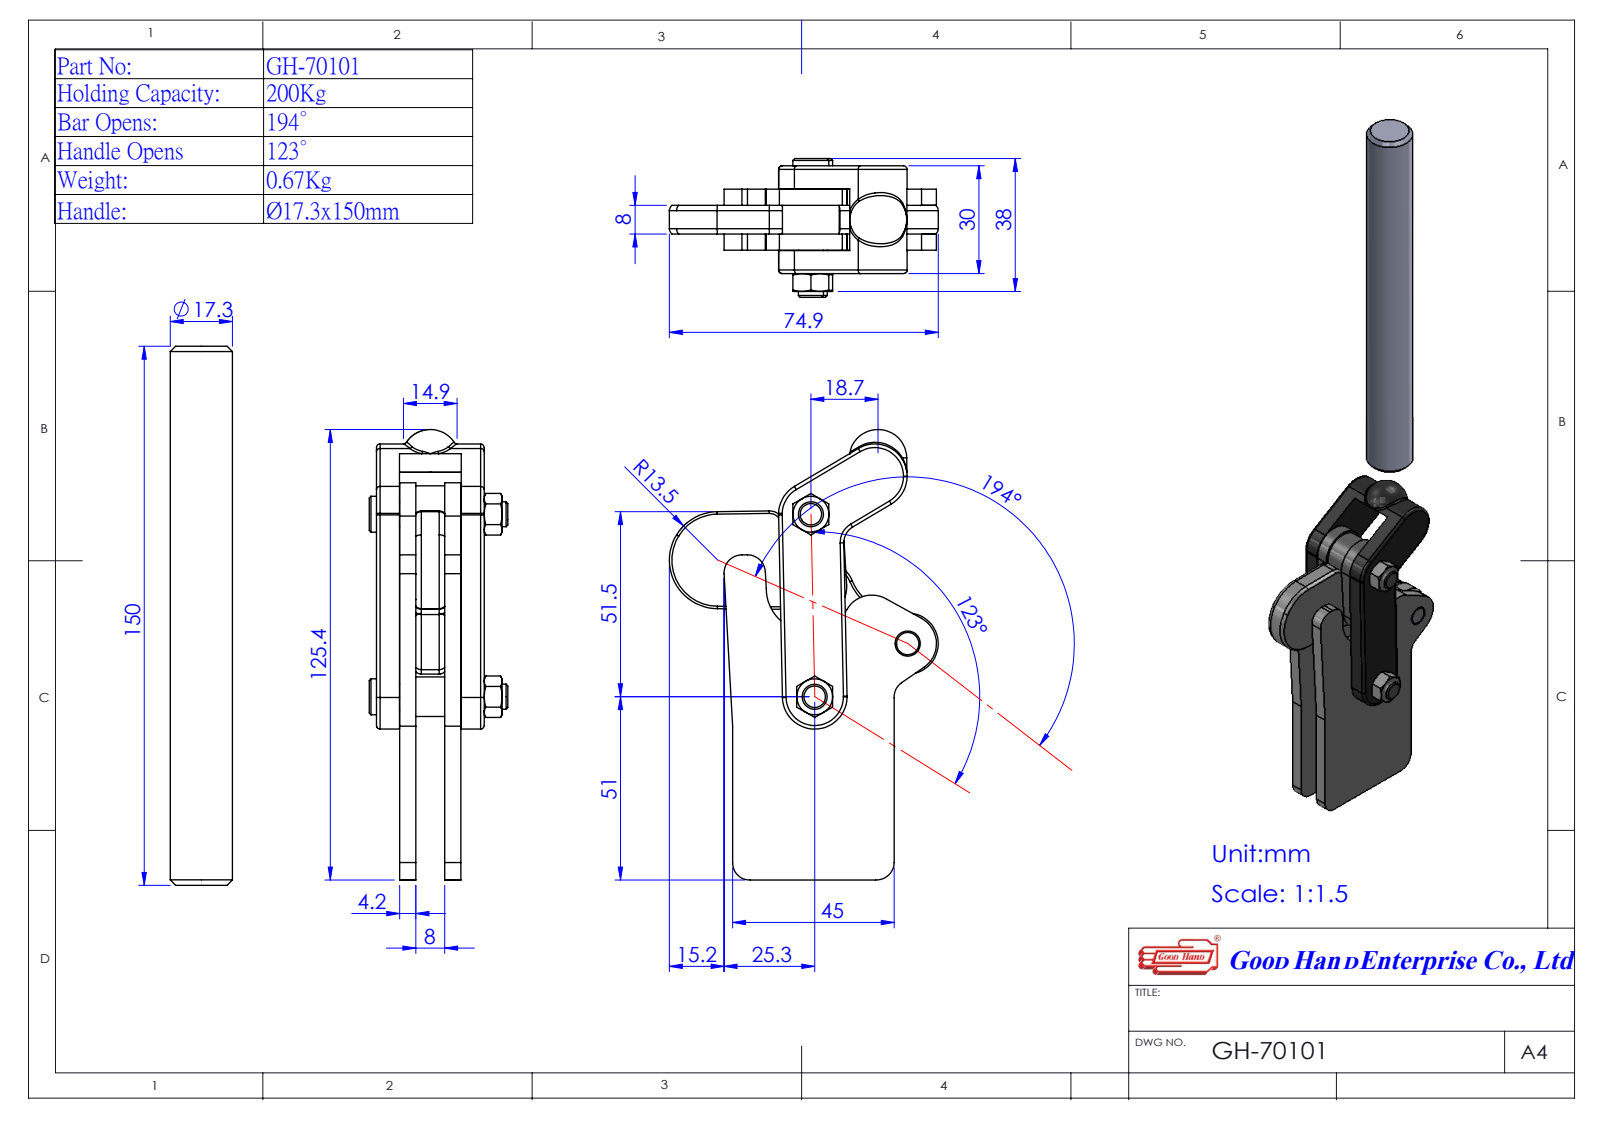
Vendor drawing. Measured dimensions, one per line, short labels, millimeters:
name: Group1^GH-70101(簡化)-1; 3700108-1^GH-70101(簡化)-1; 4702C152; Group4^GH-70101(簡化) (+2 more)
written by: SolidWorks 2016 (AUTOMOTIVE_DESIGN)
unit: mm
bodies: 5 solids, 288 faces (109 planar, 96 cylindrical, 83 other)
size: 276.97 × 74.86 × 38.6
volume: 88 317 mm³; area: 51 163 mm²
holes: 3× ⌀6.97, 1× ⌀13.9
bosses: 2× ⌀10, 1× ⌀17.3, 1× ⌀15.9, 1× ⌀6.97
rounds: 10× R1, 3× R5, 3× R9, 2× R8, 2× R8.5, 2× R8.75, 2× R9.3, 1× R4
face distances: 4.5, 12.5, 8, 17, 12.7, 17.2, 4.7, 23.5, 11, 6.3
hole spacings: 29.83, 30.2, 30.56
